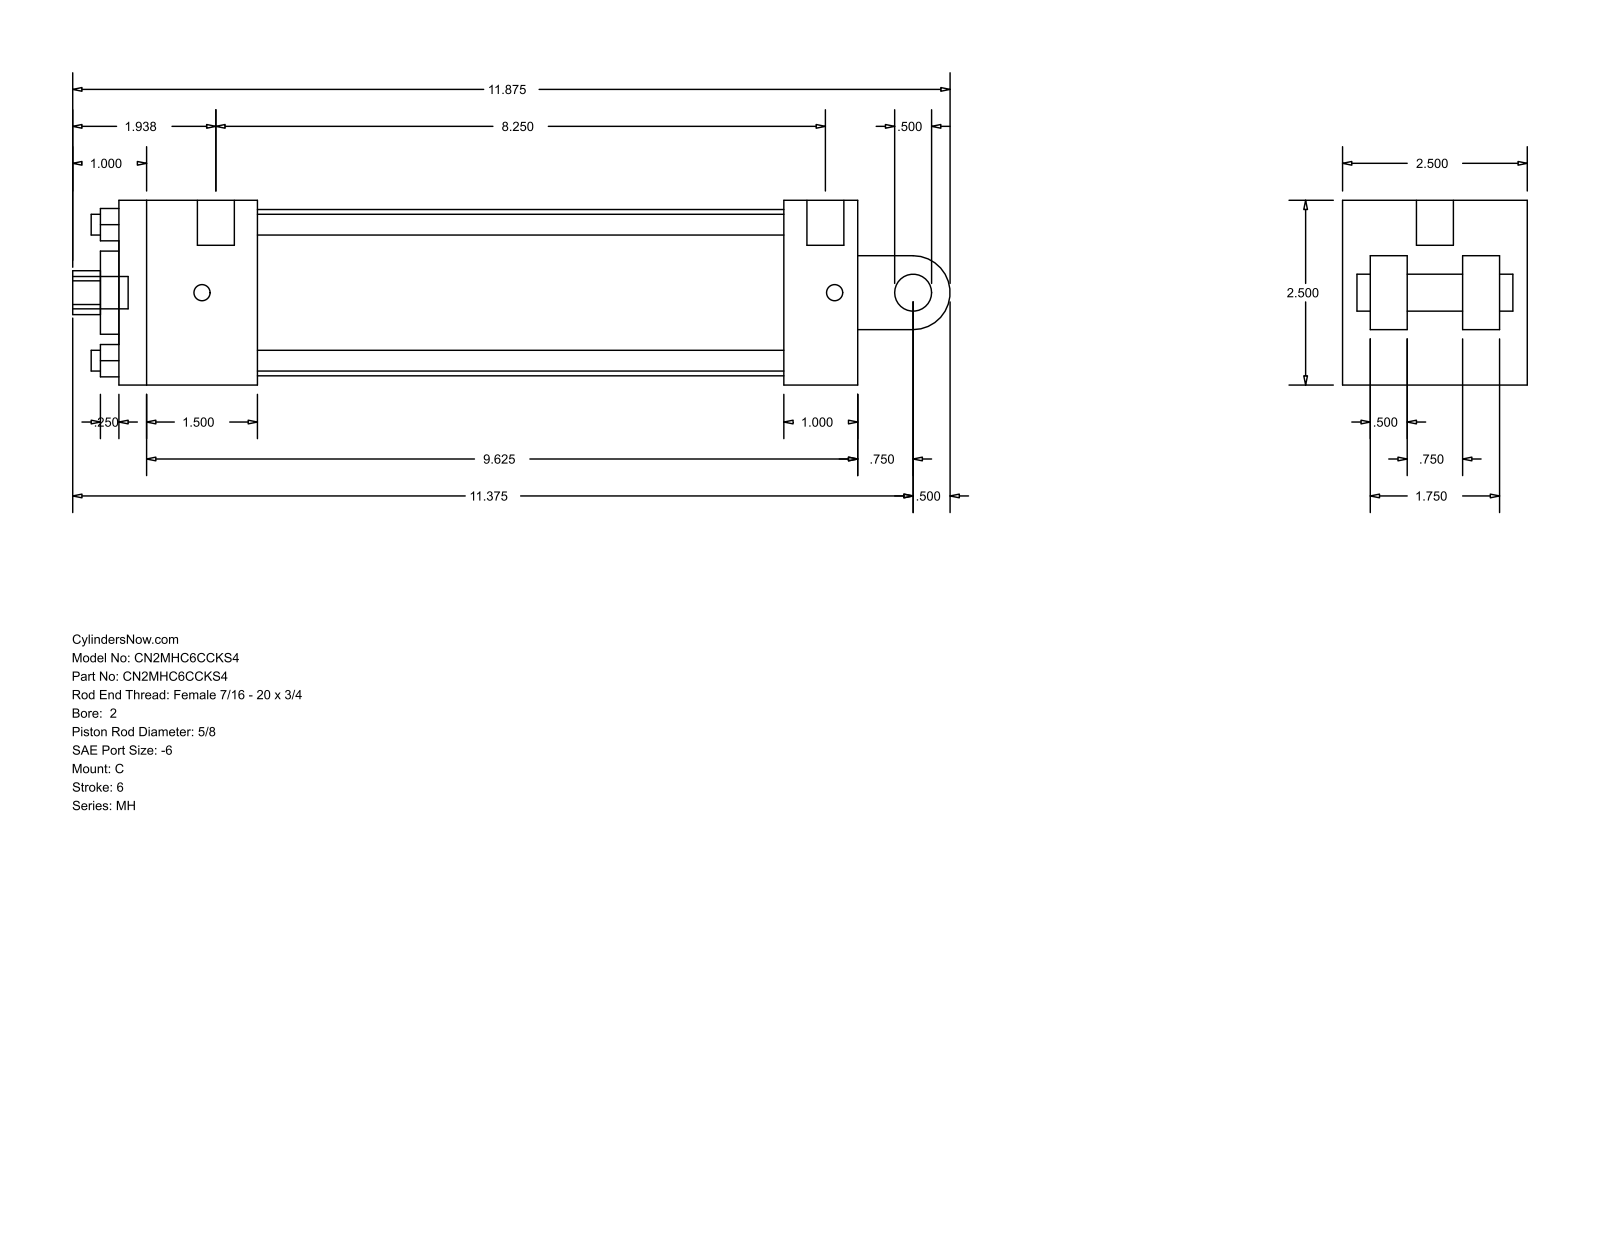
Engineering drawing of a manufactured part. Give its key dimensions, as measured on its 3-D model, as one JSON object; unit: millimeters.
{"part_name": "MH_C__0200_0.625", "step_written_by": "GSSL Pune (CONFIG_CONTROL_DESIGN)", "units": "millimeters", "bodies": {"solids": 0, "faces": 99, "planar": 70, "cylindrical": 29, "other": 0}, "overall_size": [301.62, 63.5, 63.5], "round_holes": [[7.14, 4], [5.56, 2], [12.7, 1], [15.88, 1], [28.57, 1], [57.15, 1]], "round_bosses_or_shafts": [[12.7, 2], [5.56, 2], [11.11, 1]], "partial_cylinders_radius": [[7.54, 1], [12.7, 1]], "face_to_face_distances": [63.5, 254, 12.7, 9.52, 47.62, 228.59, 180.97, 206.38, 25.41, 19.05], "hole_center_spacings": [33.05, 46.74, 66.1, 3.18]}
